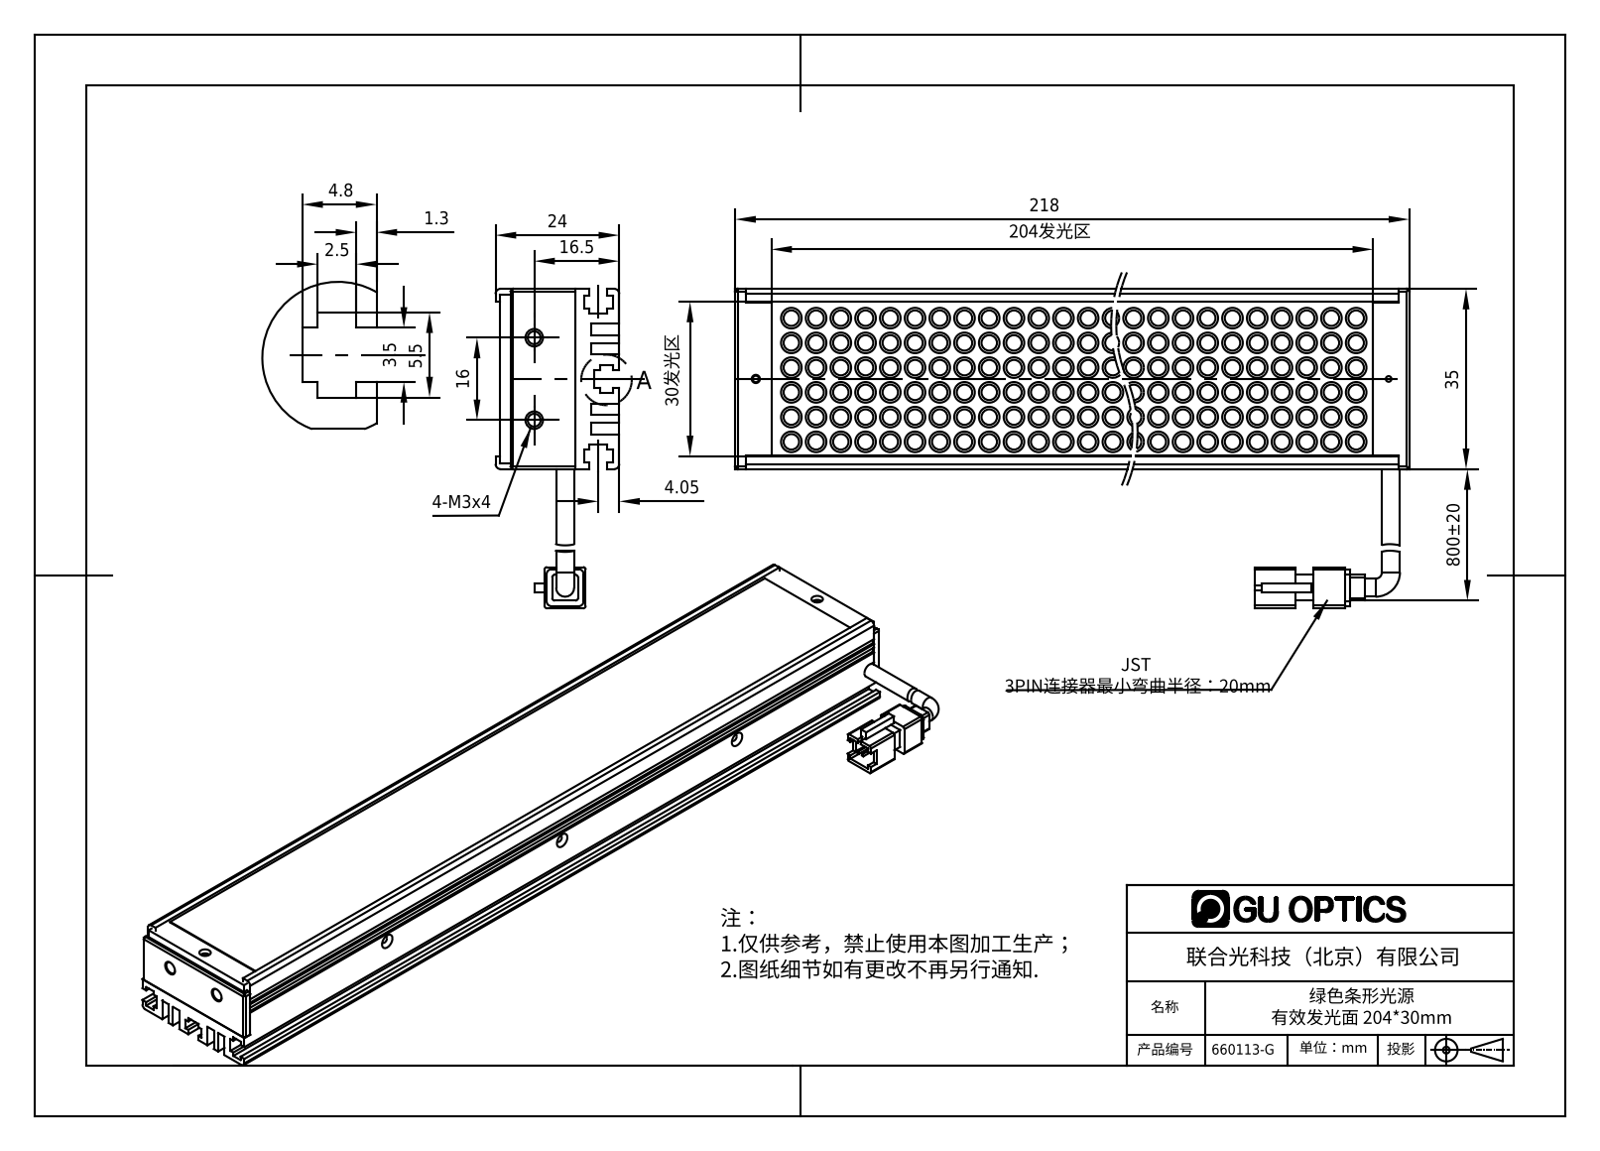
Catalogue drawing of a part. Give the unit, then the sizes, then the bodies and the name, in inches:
Units: inches
Overall size (bounding box): 8.583 × 2.441 × 0.945
Round holes (diameter × count): ⌀0.063 ×5, ⌀0.067 ×3, ⌀0.059 ×2, ⌀0.098 ×2, ⌀0.11 ×2, ⌀0.118 ×2, ⌀0.043 ×1, ⌀0.049 ×1, ⌀0.079 ×1
Round bosses / shafts (diameter × count): ⌀0.157 ×252, ⌀0.118 ×252, ⌀0.138 ×2
Partial cylindrical surfaces — rounded edges, fillets, slot ends (radius × count): R0.039 ×12, R0.02 ×8, R0.065 ×1
Main face-to-face distances: 0.079, 0.087, 0.339, 0.039, 0.098, 0.354, 0.157, 0.496, 0.575, 0.417
Hole centre spacings: 8.268, 0.276, 1.773, 1.784, 2.362, 4.134, 4.139, 6.496
Volume: 5.935 in³ · Surface area: 171.8 in²
Bodies: 8 solids, 1974 faces (520 planar, 1095 cylindrical, 359 other)
Part name (STEP PRODUCT): 660113-G
STEP written by: SolidWorks 2016 (AUTOMOTIVE_DESIGN)
